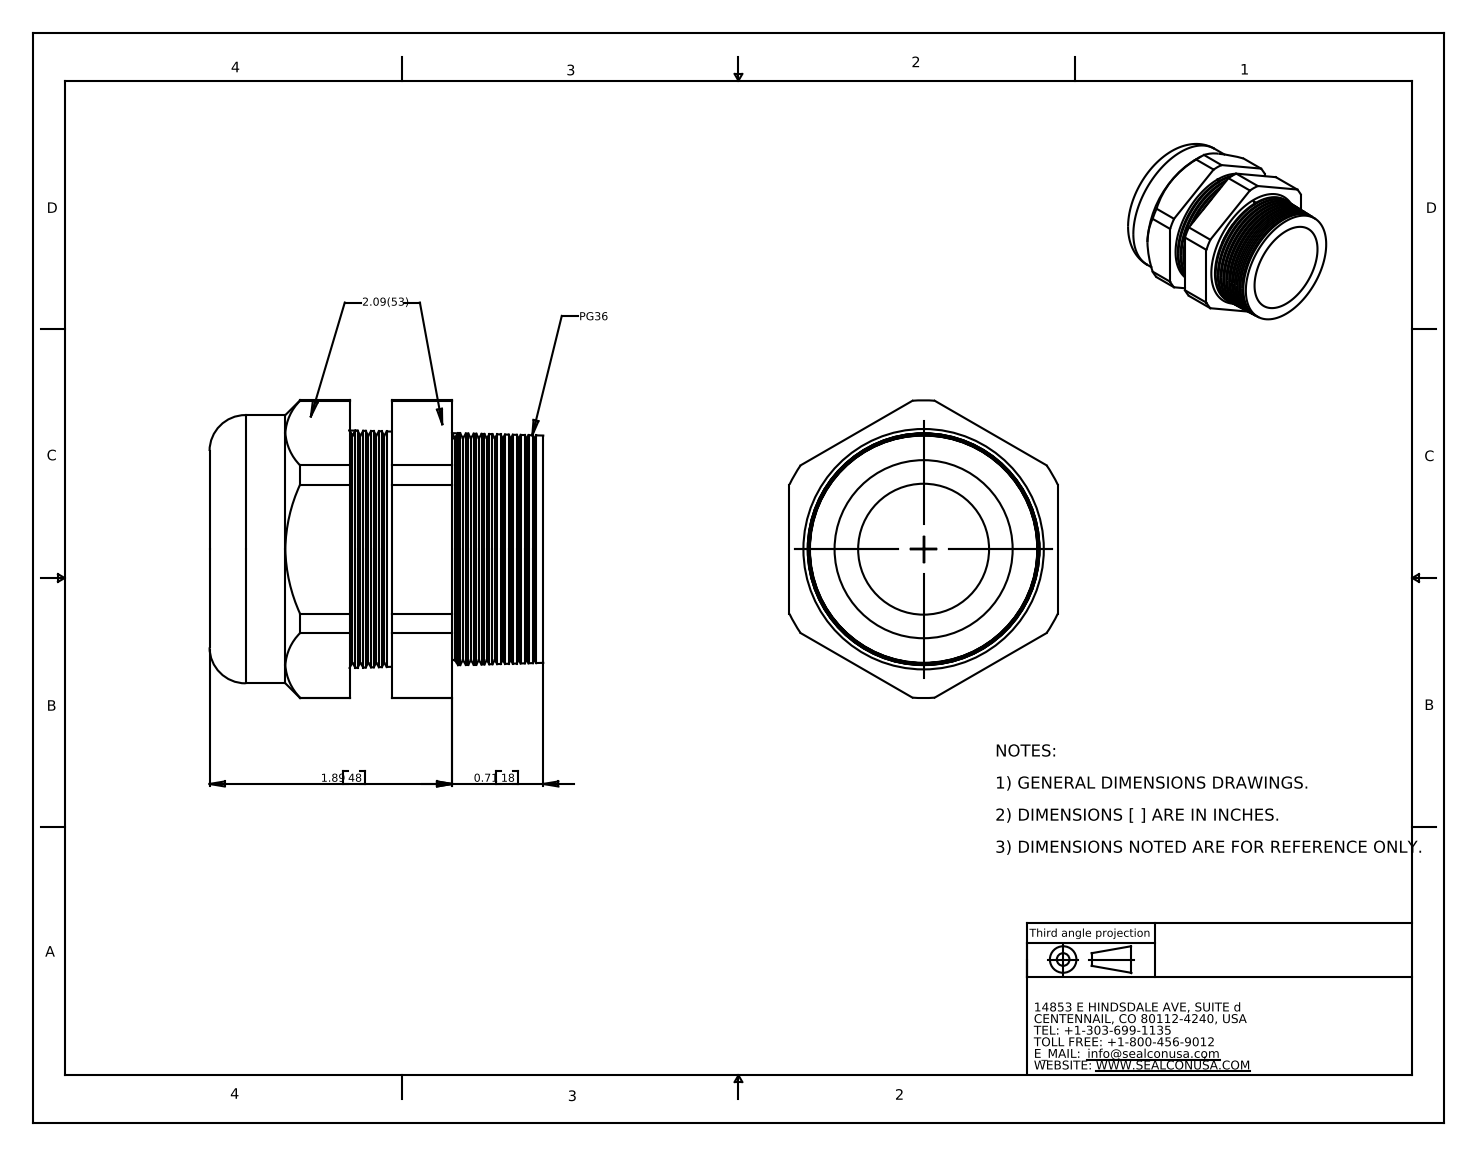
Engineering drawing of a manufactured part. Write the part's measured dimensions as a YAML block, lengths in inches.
part_name: "CD36CR-GY"
step_written_by: "SolidWorks 2007 (CONFIG_CONTROL_DESIGN)"
units: inches
bodies: {solids: 2, faces: 158, planar: 20, cylindrical: 22, other: 116}
overall_size: [2.6, 2.32, 2.09]
volume: 5.503
surface_area: 42.14
round_holes:
  - {diameter: 1.02, count: 1}
  - {diameter: 1.387, count: 1}
round_bosses_or_shafts:
  - {diameter: 2.09, count: 1}
partial_cylinders:
  - {radius: 1.16, count: 1}
face_to_face_distances: [2.09, 0.827, 0.5, 0.327, 1.3, 0.8, 0.472, 2.009, 1.509, 1.182]
